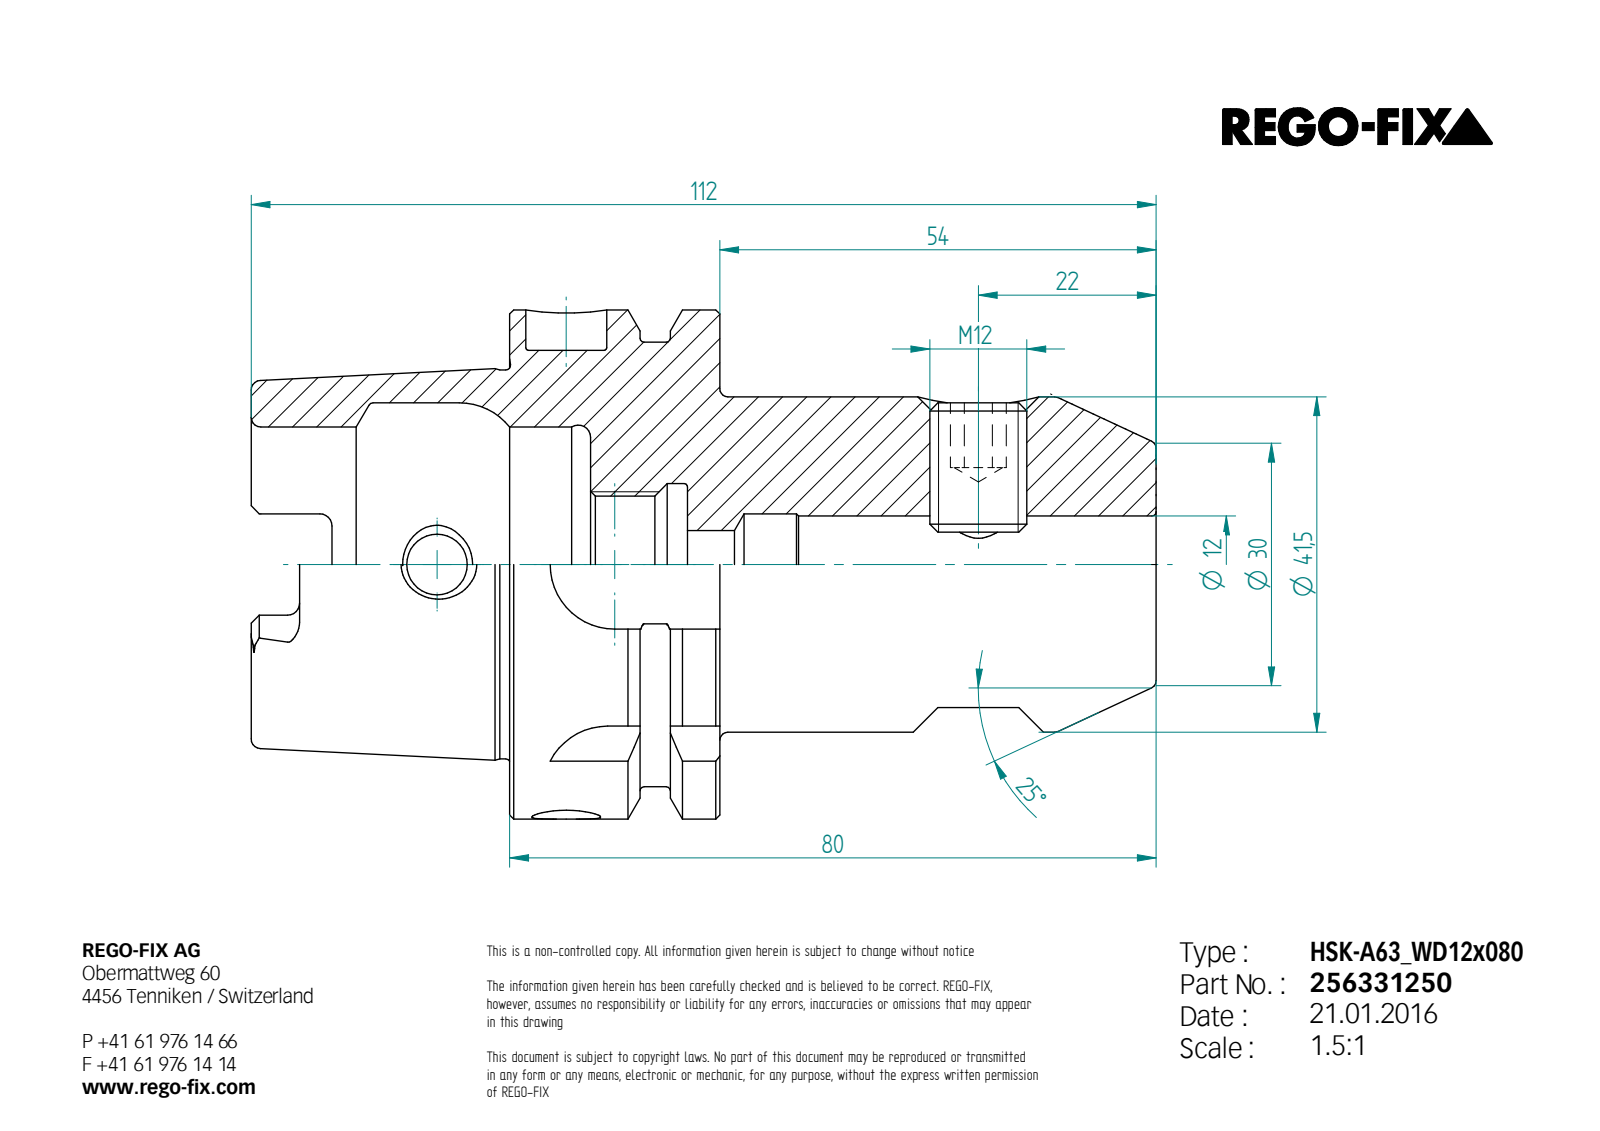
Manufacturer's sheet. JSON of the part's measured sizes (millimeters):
{"step_written_by": "Unknown (AUTOMOTIVE_DESIGN)", "units": "millimeters", "bodies": {"solids": 1, "faces": 129, "planar": 47, "cylindrical": 33, "other": 49}, "overall_size": [97, 63, 63], "volume_mm3": 110970, "surface_area_mm2": 27442, "round_holes": [[10, 2], [7.5, 1], [8.38, 1], [8.5, 1], [16.92, 1], [20, 1], [34, 1], [40, 1]], "round_bosses_or_shafts": [[63, 1], [55, 1], [48.13, 1], [34.5, 1]], "partial_cylinders_radius": [[1.5, 6], [2.88, 4], [8, 4]], "face_to_face_distances": [26, 10, 16, 32, 65, 55, 39, 42, 58, 97], "hole_center_spacings": [38.5]}
